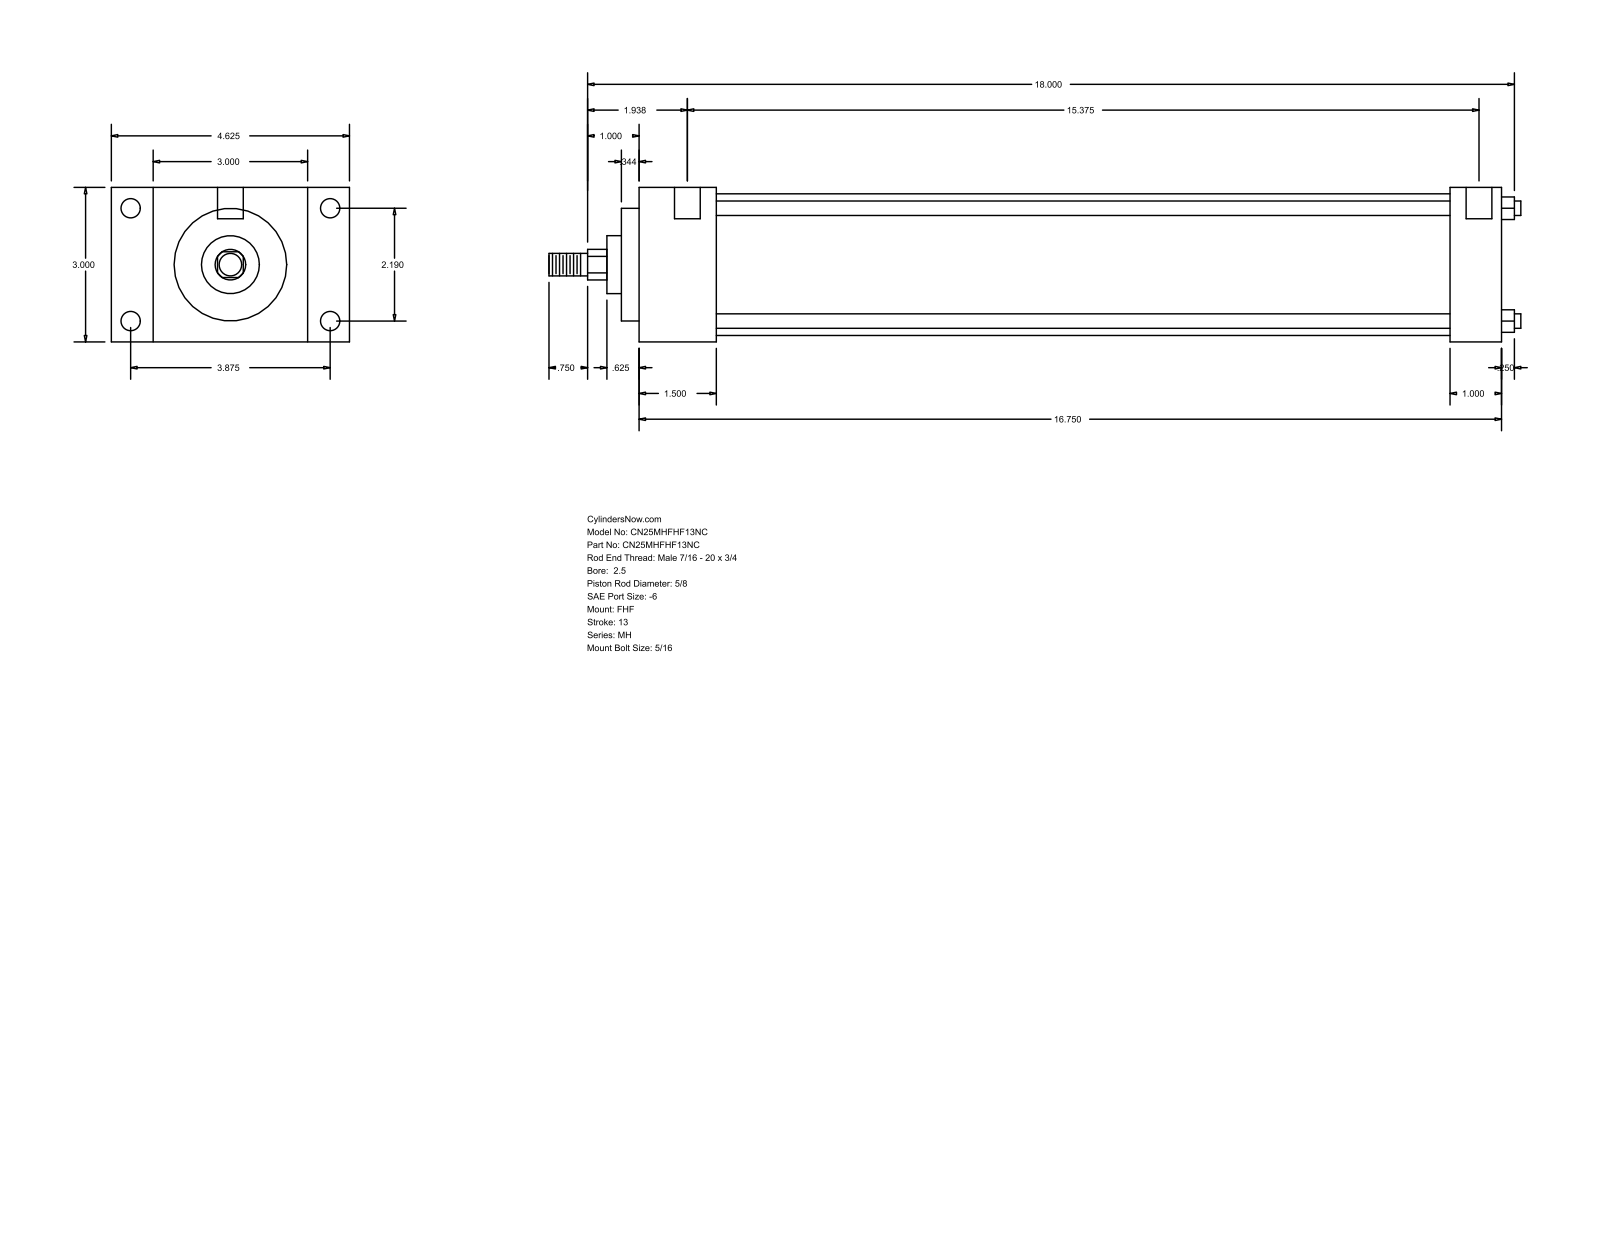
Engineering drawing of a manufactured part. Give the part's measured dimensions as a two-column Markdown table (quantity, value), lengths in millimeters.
| quantity | value |
| --- | --- |
| part name | MH_FHF__0250_0.625 |
| STEP written by | GSSL Pune (CONFIG_CONTROL_DESIGN) |
| units | millimeters |
| bodies | 0 solids, 90 faces (61 planar, 29 cylindrical, 0 other) |
| overall size | 479.43 × 117.47 × 76.2 |
| round holes (diameter × count) | 5.56 × 4, 9.53 × 4, 12.7 × 2 |
| round bosses / shafts (diameter × count) | 7.14 × 4, 69.85 × 1, 55.55 × 1, 28.57 × 1, 15.88 × 1, 11.11 × 1 |
| partial cylindrical surfaces (radius × count) | 7.54 × 1 |
| main face-to-face distances | 76.2, 425.45, 38.1, 387.35, 20.64, 96.84, 117.48, 25.4, 400.05, 361.95 |
| hole center spacings | 55.62, 98.42, 113.05, 398.46, 3.17, 4.76, 390.53, 393.7 |
